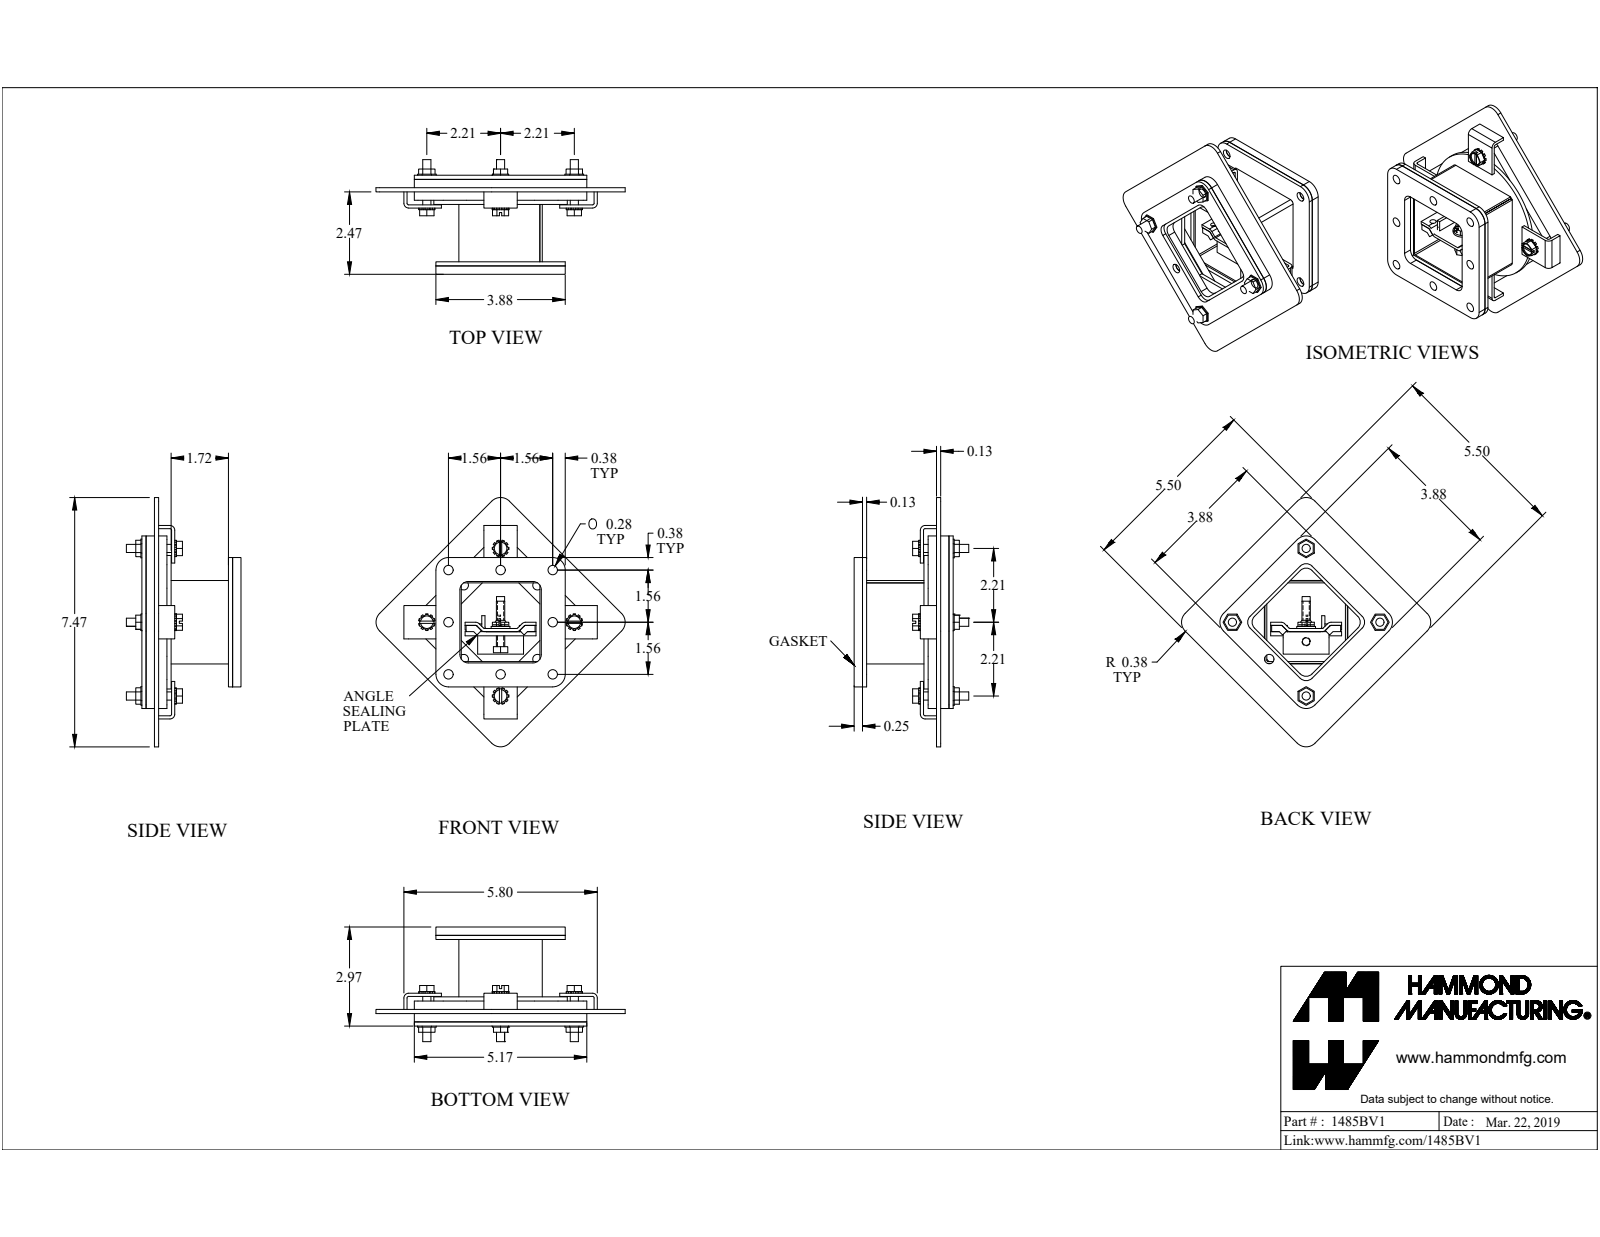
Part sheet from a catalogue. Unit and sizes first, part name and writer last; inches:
Units: inches
Overall size (bounding box): 7.468 × 7.468 × 3.434
Round holes (diameter × count): ⌀0.281 ×16, ⌀0.375 ×6, ⌀0.196 ×5, ⌀0.258 ×4, ⌀0.312 ×4, ⌀0.187 ×2, ⌀0.224 ×1, ⌀0.265 ×1, ⌀0.313 ×1
Round bosses / shafts (diameter × count): ⌀0.244 ×5, ⌀4 ×1, ⌀0.563 ×1, ⌀0.25 ×1
Partial cylindrical surfaces — rounded edges, fillets, slot ends (radius × count): R0.25 ×16, R0.375 ×12, R0.048 ×9, R0.143 ×9, R0.062 ×4, R0.036 ×3, R0.108 ×3, R0.06 ×1
Main face-to-face distances: 0.25, 2.593, 0.125, 0.375, 0.125, 2.218, 0.375, 2.343, 2.093, 1.843
Hole centre spacings: 2.706, 1.563, 1.691, 4.083, 3.125, 1.196, 2.887, 3.494
Volume: 15.51 in³ · Surface area: 265.2 in²
Bodies: 32 solids, 647 faces (447 planar, 188 cylindrical, 12 other)
Part name (STEP PRODUCT): 1485BV1
STEP written by: SolidWorks 2019 (CONFIG_CONTROL_DESIGN)
